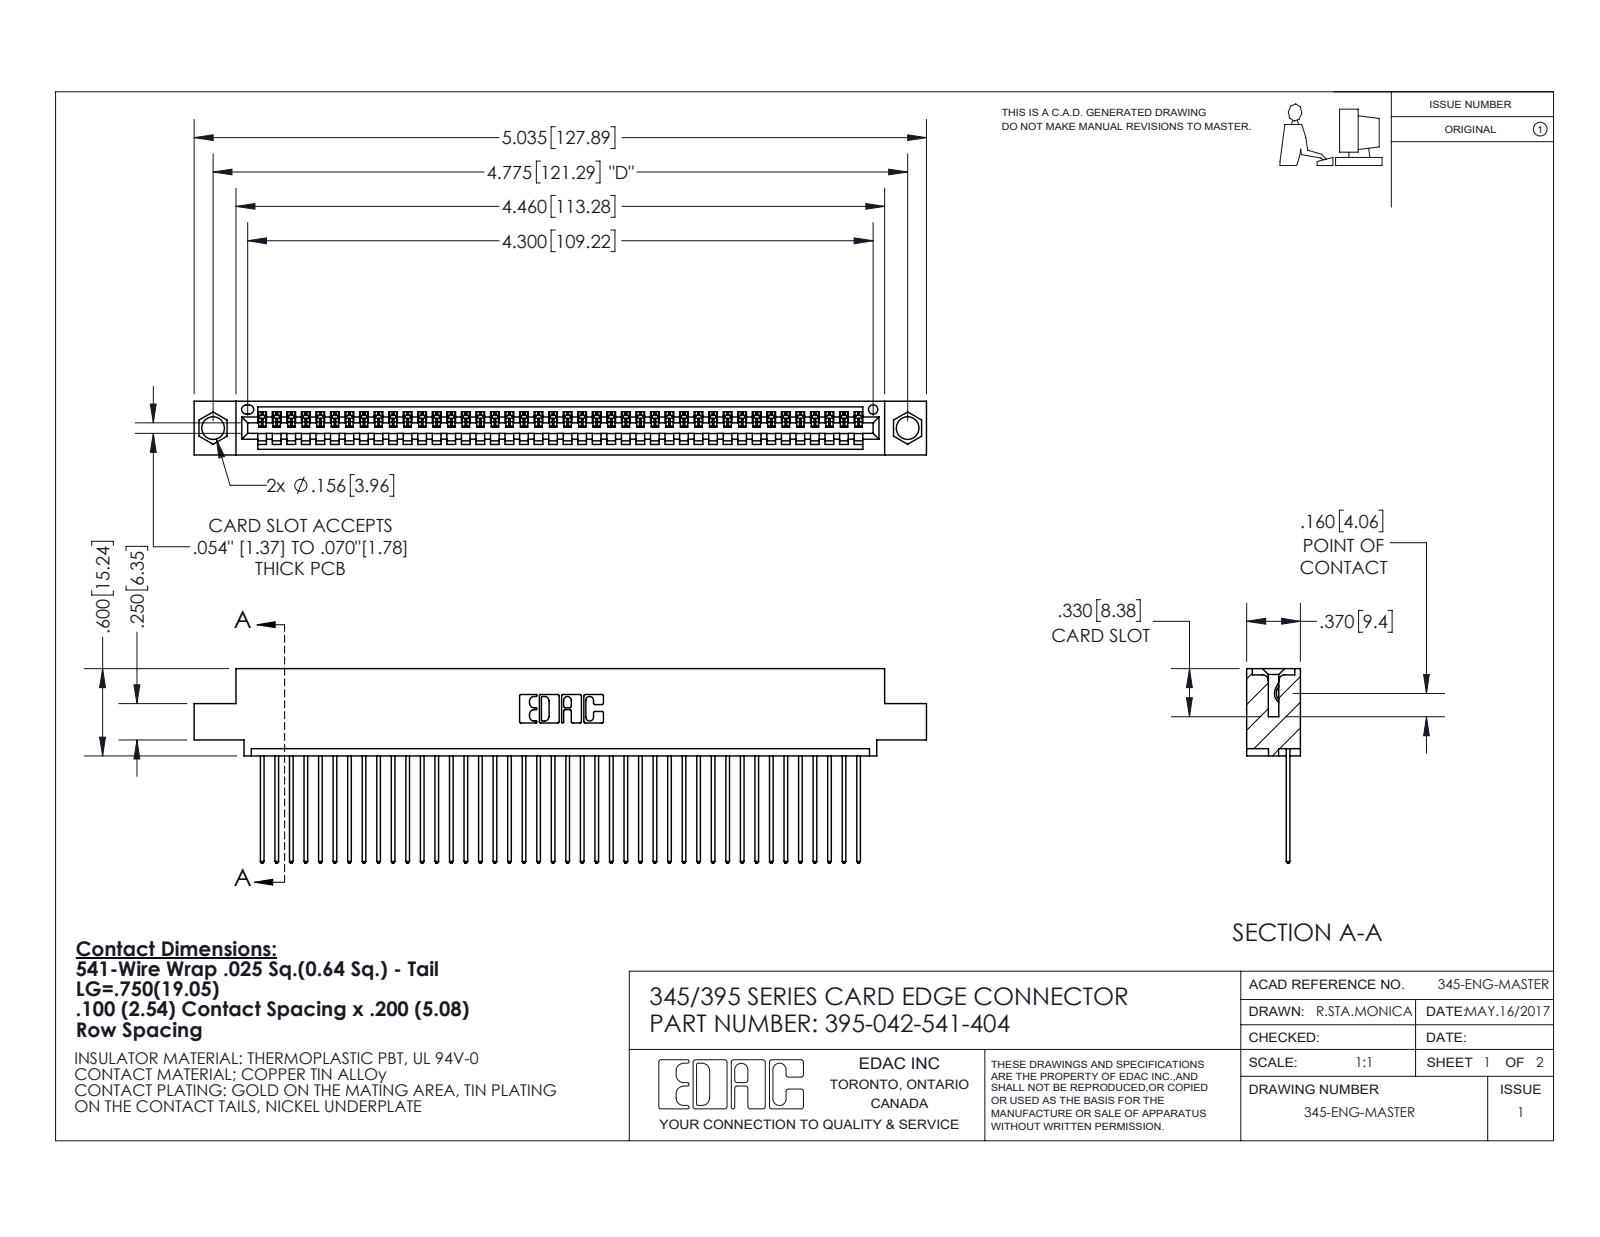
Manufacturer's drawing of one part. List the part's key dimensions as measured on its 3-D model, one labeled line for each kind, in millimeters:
Part name (STEP PRODUCT): 395-042-541-404; 345-292-001_345-293-141; 345 Part_0.110 Offset - 0.156 Dia-TI
STEP written by: SolidWorks 2020 (CONFIG_CONTROL_DESIGN)
Units: millimetres
Bodies: 43 solids, 2580 faces (1778 planar, 802 cylindrical, 0 other)
Overall size (bounding box): 127.9 × 34 × 9.4
Volume: 12 100 mm³ · Surface area: 16 830 mm²
Round holes (diameter × count): ⌀4 ×2, ⌀1.6 ×1
Partial cylindrical surfaces — rounded edges, fillets, slot ends (radius × count): R0.2 ×84, R0.3 ×84, R0.3 ×22, R0.2 ×6, R0.8 ×6, R0.7 ×3, R0.8 ×2, R1 ×2
Main face-to-face distances: 1.8, 7.6, 2.5, 6.9, 0.6, 9.4, 5.1, 5.7, 3.8, 1.8
Hole centre spacings: 6.9, 115.3, 121.3
